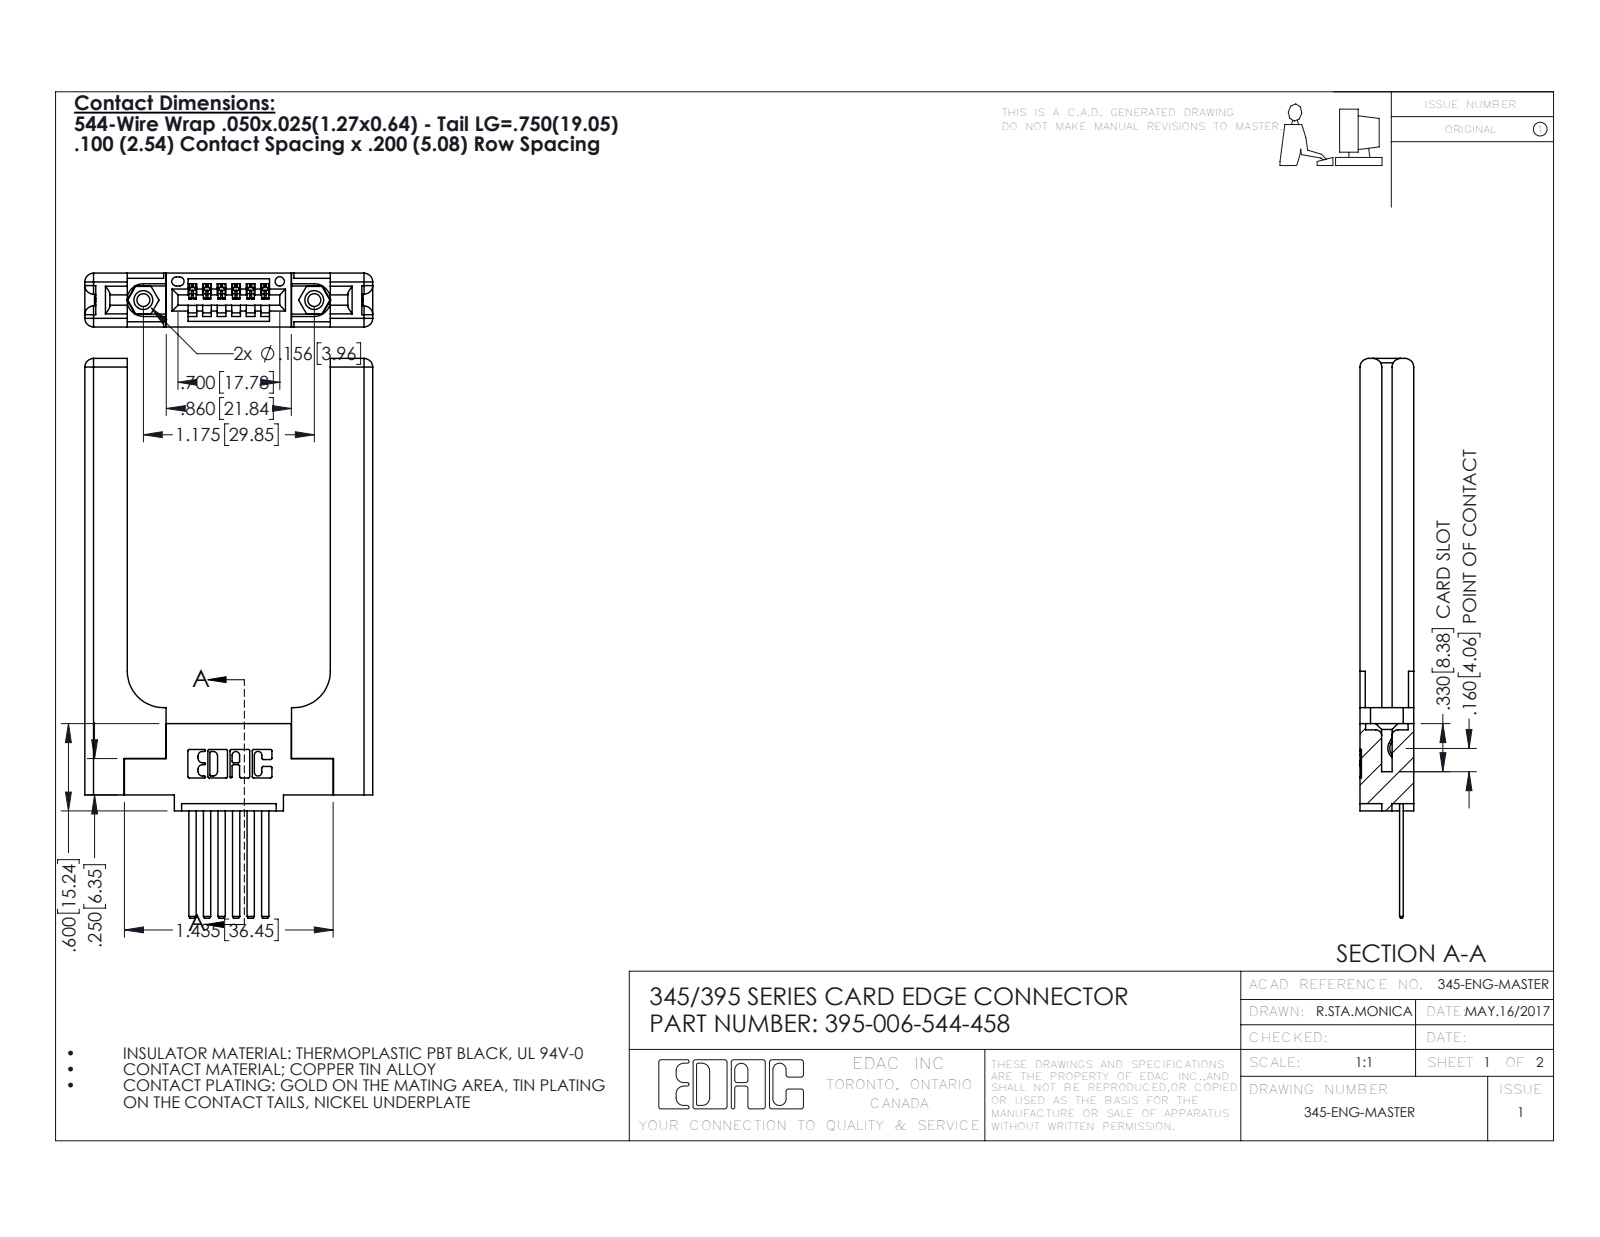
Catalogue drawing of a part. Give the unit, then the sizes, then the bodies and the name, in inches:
Units: inches
Overall size (bounding box): 3.847 × 1.979 × 0.37
Round holes (diameter × count): ⌀0.089 ×2, ⌀0.125 ×2, ⌀0.156 ×2, ⌀0.064 ×1
Round bosses / shafts (diameter × count): ⌀0.155 ×2
Partial cylindrical surfaces — rounded edges, fillets, slot ends (radius × count): R0.01 ×22, R0.06 ×16, R0.006 ×12, R0.007 ×6, R0.031 ×6, R0.026 ×3, R0.03 ×2, R0.031 ×2
Main face-to-face distances: 0.37, 0.15, 0.22, 0.072, 0.148, 0.077, 0.298, 1.396, 0.071, 0.292
Hole centre spacings: 0.27, 0.946, 1.175
Volume: 0.792 in³ · Surface area: 17.13 in²
Bodies: 11 solids, 698 faces (448 planar, 190 cylindrical, 60 other)
Part name (STEP PRODUCT): 345-250-001_345-250-001-102; 395-006-544-458; 345-292-001_345-293-144; 345 Part_0.110 Offset - 0.156 Dia-TH (+1 more)
STEP written by: SolidWorks 2016 (CONFIG_CONTROL_DESIGN)
